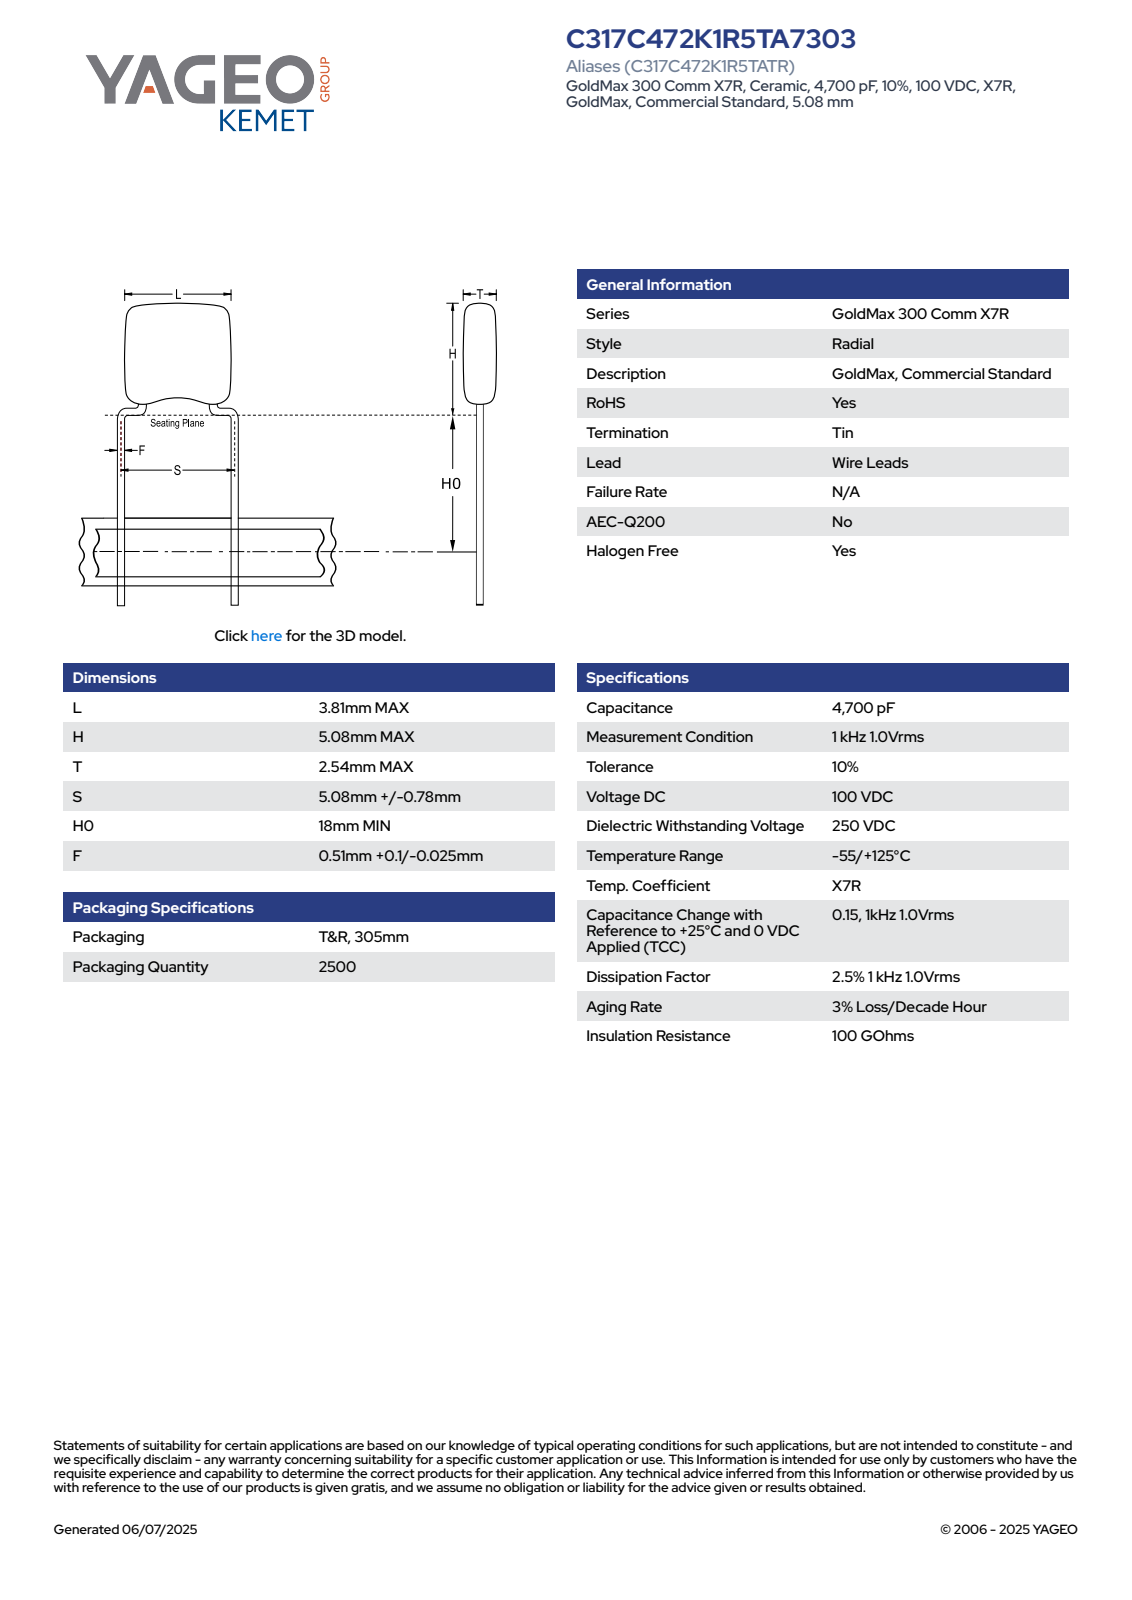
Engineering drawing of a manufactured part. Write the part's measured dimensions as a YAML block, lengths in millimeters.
part_name: "CCR_SB_3.81X5.08_L3.81H5.08T2.54S5.08H018F0.51"
step_written_by: "SolidWorks 2014 (AUTOMOTIVE_DESIGN)"
units: millimeters
bodies: {solids: 4, faces: 97, planar: 65, cylindrical: 14, other: 18}
overall_size: [23.08, 5.59, 2.54]
volume: 37
surface_area: 115
round_bosses_or_shafts:
  - {diameter: 0.51, count: 2}
partial_cylinders:
  - {radius: 1, count: 10}
face_to_face_distances: [2.54, 3.81, 3.61, 1.95, 1.66, 1.63, 0.32, 1.98, 0.66, 0.33]
